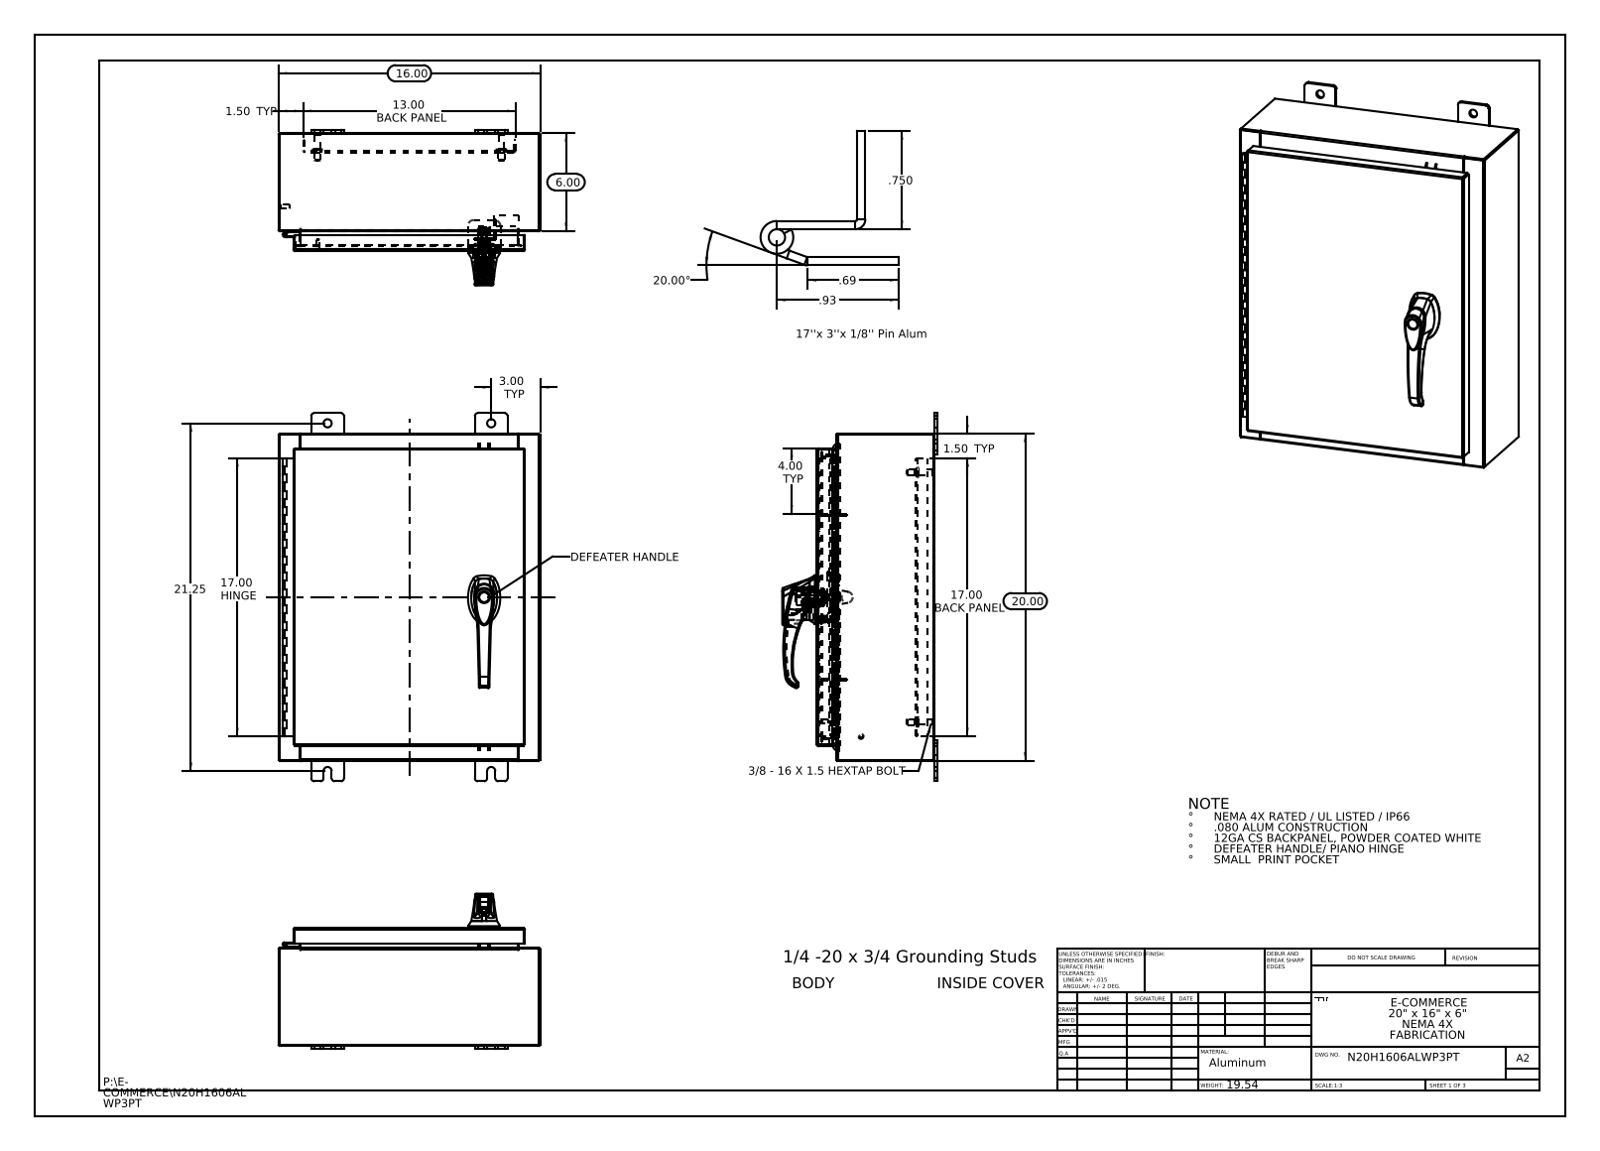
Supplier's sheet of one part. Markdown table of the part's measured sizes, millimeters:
| quantity | value |
| --- | --- |
| part name | N20H1606ALWP3PT Bottom; 022151; 297026; N20H1606ALWP3PT 263033_Industrilas (+8 more) |
| STEP written by | SolidWorks 2013 (CONFIG_CONTROL_DESIGN) |
| units | millimeters |
| bodies | 37 solids, 2402 faces (835 planar, 869 cylindrical, 698 other) |
| overall size | 571.5 × 406.4 × 241.2 |
| volume | 2 161 000 mm³ |
| surface area | 2 086 000 mm² |
| round holes (diameter × count) | 12.7 × 8, 6.4 × 4, 3.5 × 3, 4.1 × 3, 2 × 2, 5.2 × 2, 8 × 2, 11.1 × 2, 3.2 × 1, 3.2 × 1, 5 × 1, 7 × 1 |
| round bosses / shafts (diameter × count) | 15.9 × 4, 9.5 × 4, 8.4 × 4, 4 × 4, 3.6 × 4, 8 × 3, 6 × 3, 30 × 1 |
| partial cylindrical surfaces (radius × count) | 3 × 37, 0.2 × 33, 4.8 × 24, 0.3 × 22, 2.2 × 18, 1 × 15, 0.7 × 12, 0.2 × 6 |
| main face-to-face distances | 1.9, 181, 179.1, 182.9, 2.6, 404.5, 25.4, 27.3, 153.7, 155.6 |
| hole center spacings | 86.5, 304.2, 7.5, 15.9, 21.4, 31.8, 33.4, 39.6 |
